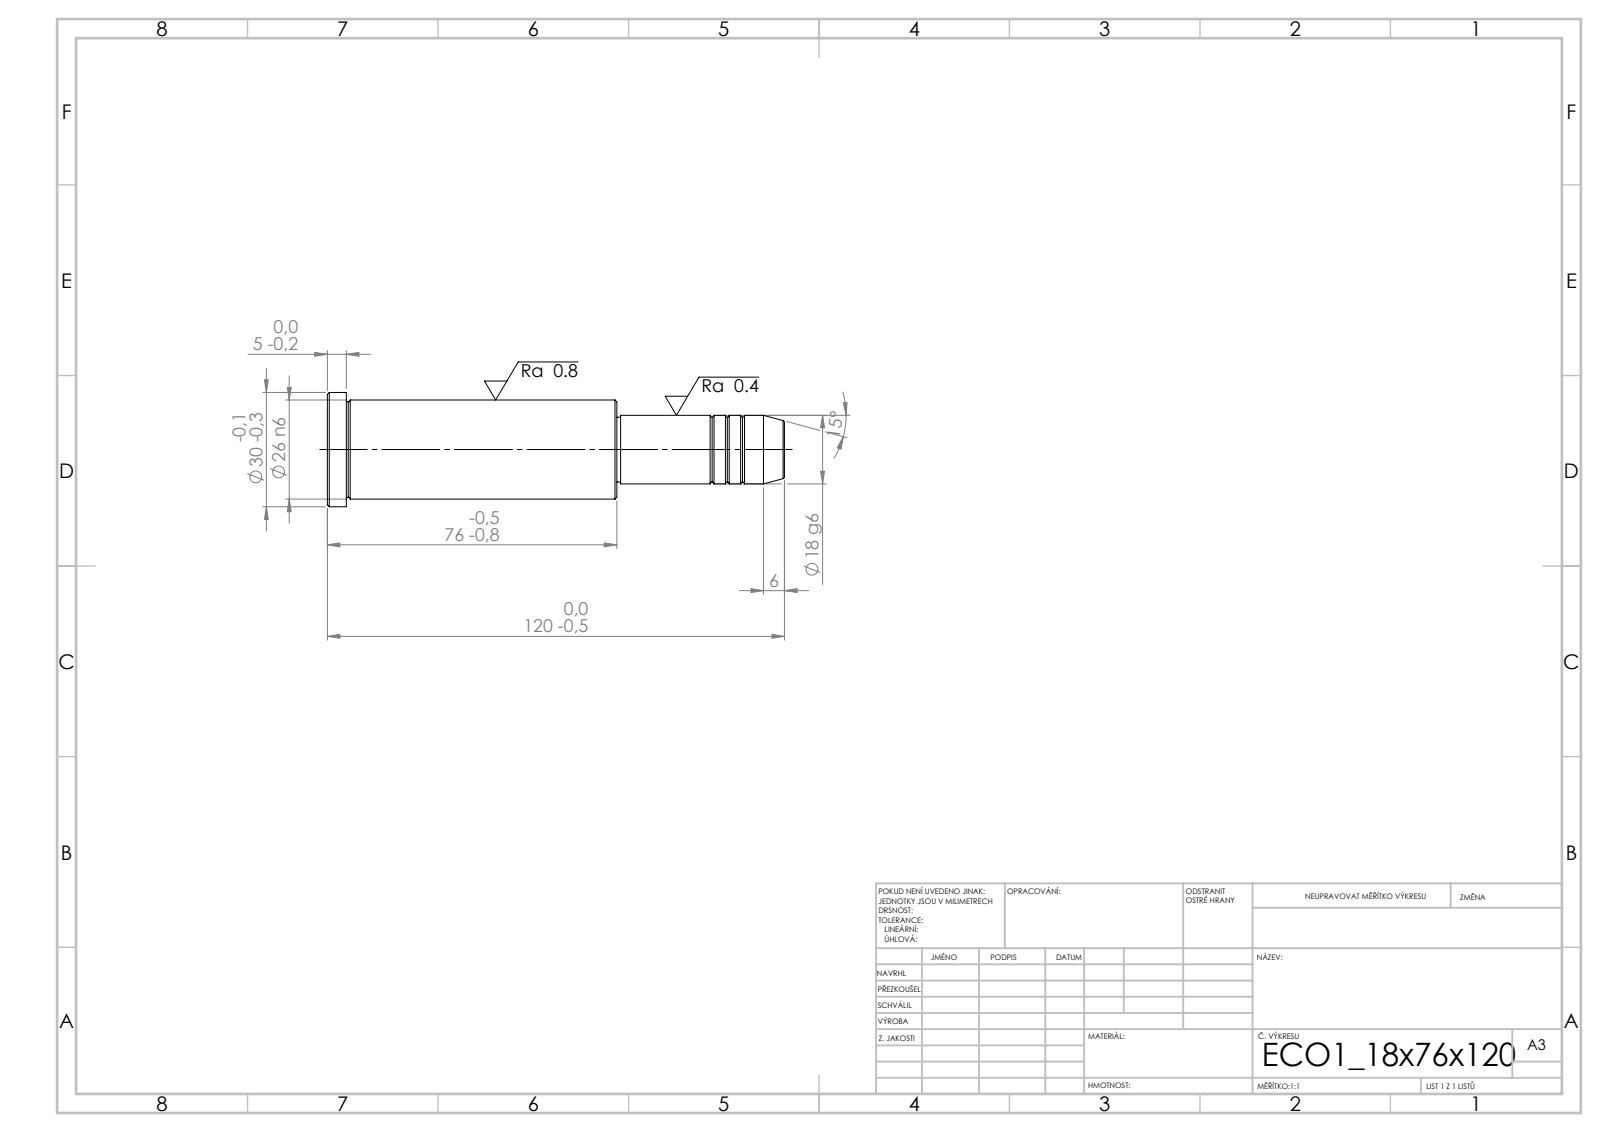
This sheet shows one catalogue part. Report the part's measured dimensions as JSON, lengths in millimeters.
{"step_written_by": "SolidWorks 2019 (CONFIG_CONTROL_DESIGN)", "units": "millimeters", "bodies": {"solids": 1, "faces": 43, "planar": 5, "cylindrical": 14, "other": 24}, "overall_size": [120, 30, 30], "volume_mm3": 52063, "surface_area_mm2": 10206, "round_bosses_or_shafts": [[30, 1], [26, 1], [18, 1], [17, 1]], "face_to_face_distances": [76, 71, 5, 44, 115, 120, 43, 1, 72, 77]}
